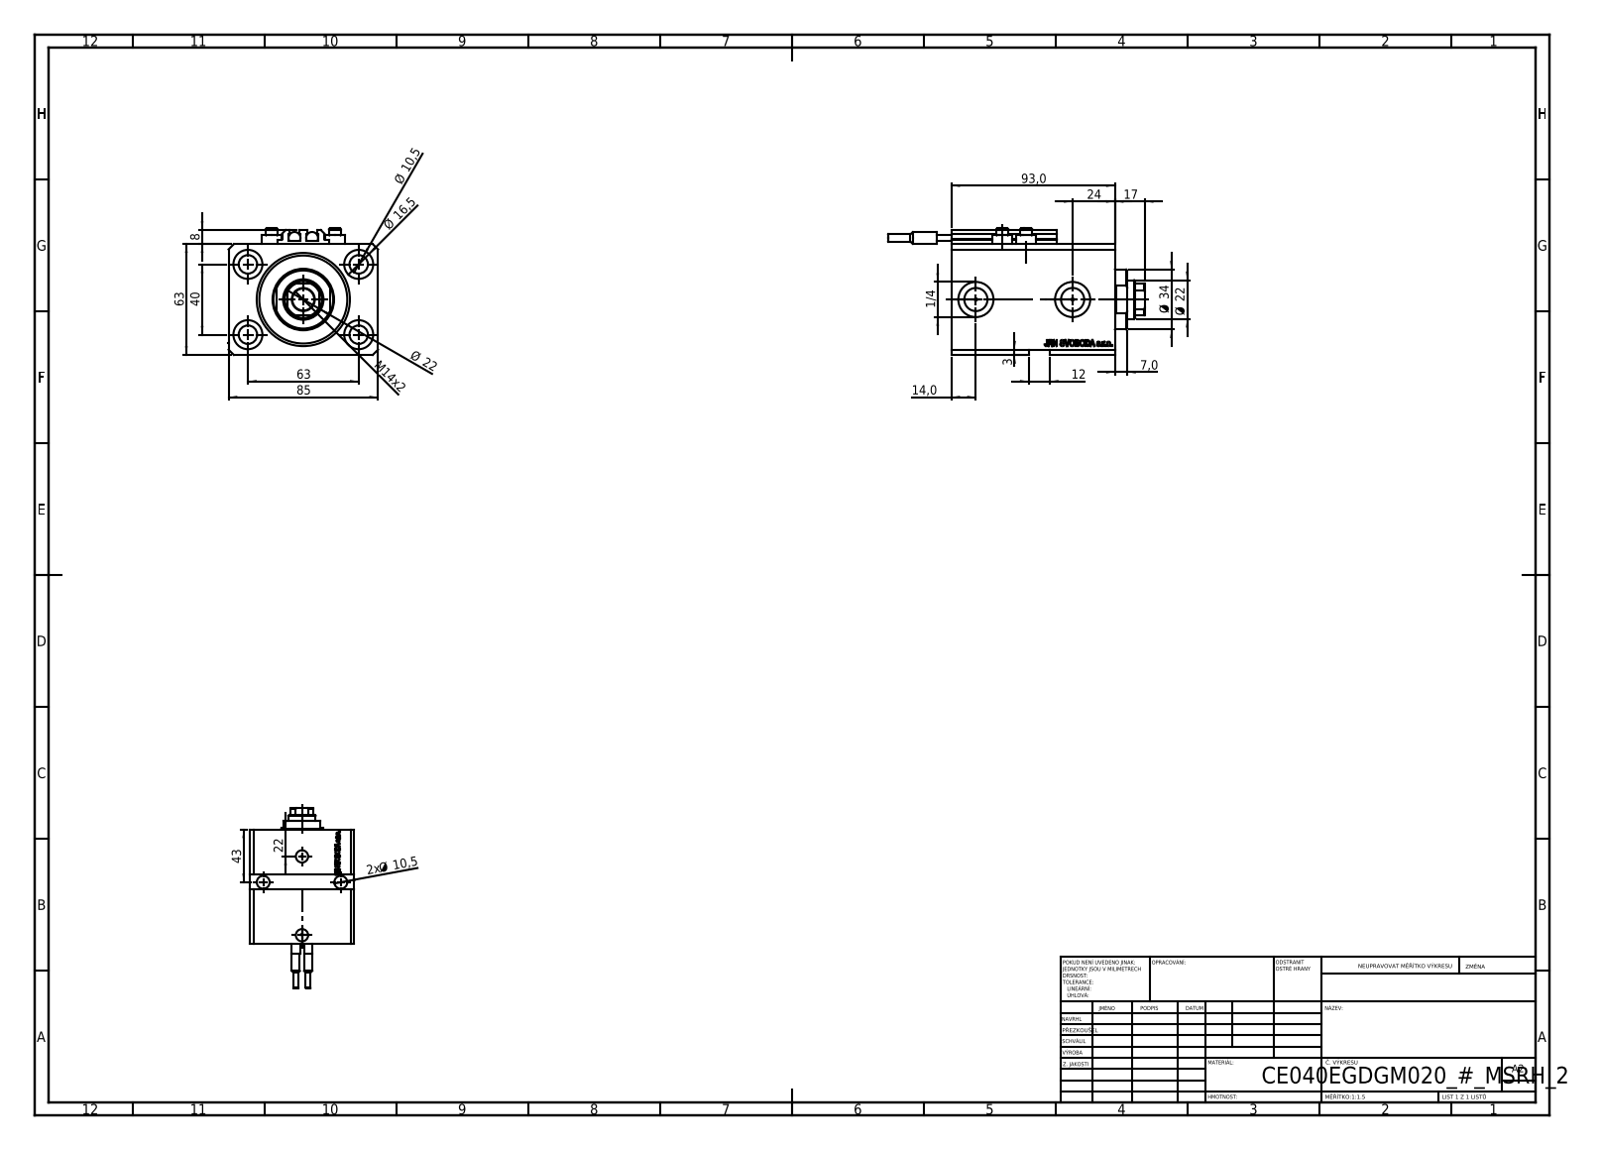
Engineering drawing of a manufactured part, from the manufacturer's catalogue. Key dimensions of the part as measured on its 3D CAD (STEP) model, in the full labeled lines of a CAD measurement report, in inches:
Part name (STEP PRODUCT): SWITCH_V250CE; V250CE_VC_E; V250CE_C_VCP; ALLEN BOLT V250CE (+1 more)
STEP written by: SolidWorks 2019 (CONFIG_CONTROL_DESIGN)
Units: inches
Bodies: 10 solids, 1155 faces (571 planar, 150 cylindrical, 434 other)
Overall size (bounding box): 5.748 × 3.346 × 2.835
Volume: 26.68 in³ · Surface area: 154.5 in²
Round holes (diameter × count): ⌀0.413 ×6, ⌀0.049 ×4, ⌀0.157 ×4, ⌀0.65 ×4, ⌀0.394 ×2, ⌀0.518 ×2, ⌀0.787 ×2, ⌀0.492 ×1, ⌀0.866 ×1, ⌀1.575 ×1, ⌀2.087 ×1
Round bosses / shafts (diameter × count): ⌀0.457 ×4, ⌀0.276 ×4, ⌀0.268 ×2, ⌀0.256 ×2, ⌀0.157 ×2, ⌀1.339 ×1
Partial cylindrical surfaces — rounded edges, fillets, slot ends (radius × count): R0.008 ×10, R0.413 ×1
Main face-to-face distances: 2.48, 3.346, 3.661, 0.669, 2.992, 0.449, 2.543, 3.213, 0.118, 2.559
Hole centre spacings: 1.469, 2.48, 0.535, 0.606, 0.983, 1.103, 1.119, 1.324
